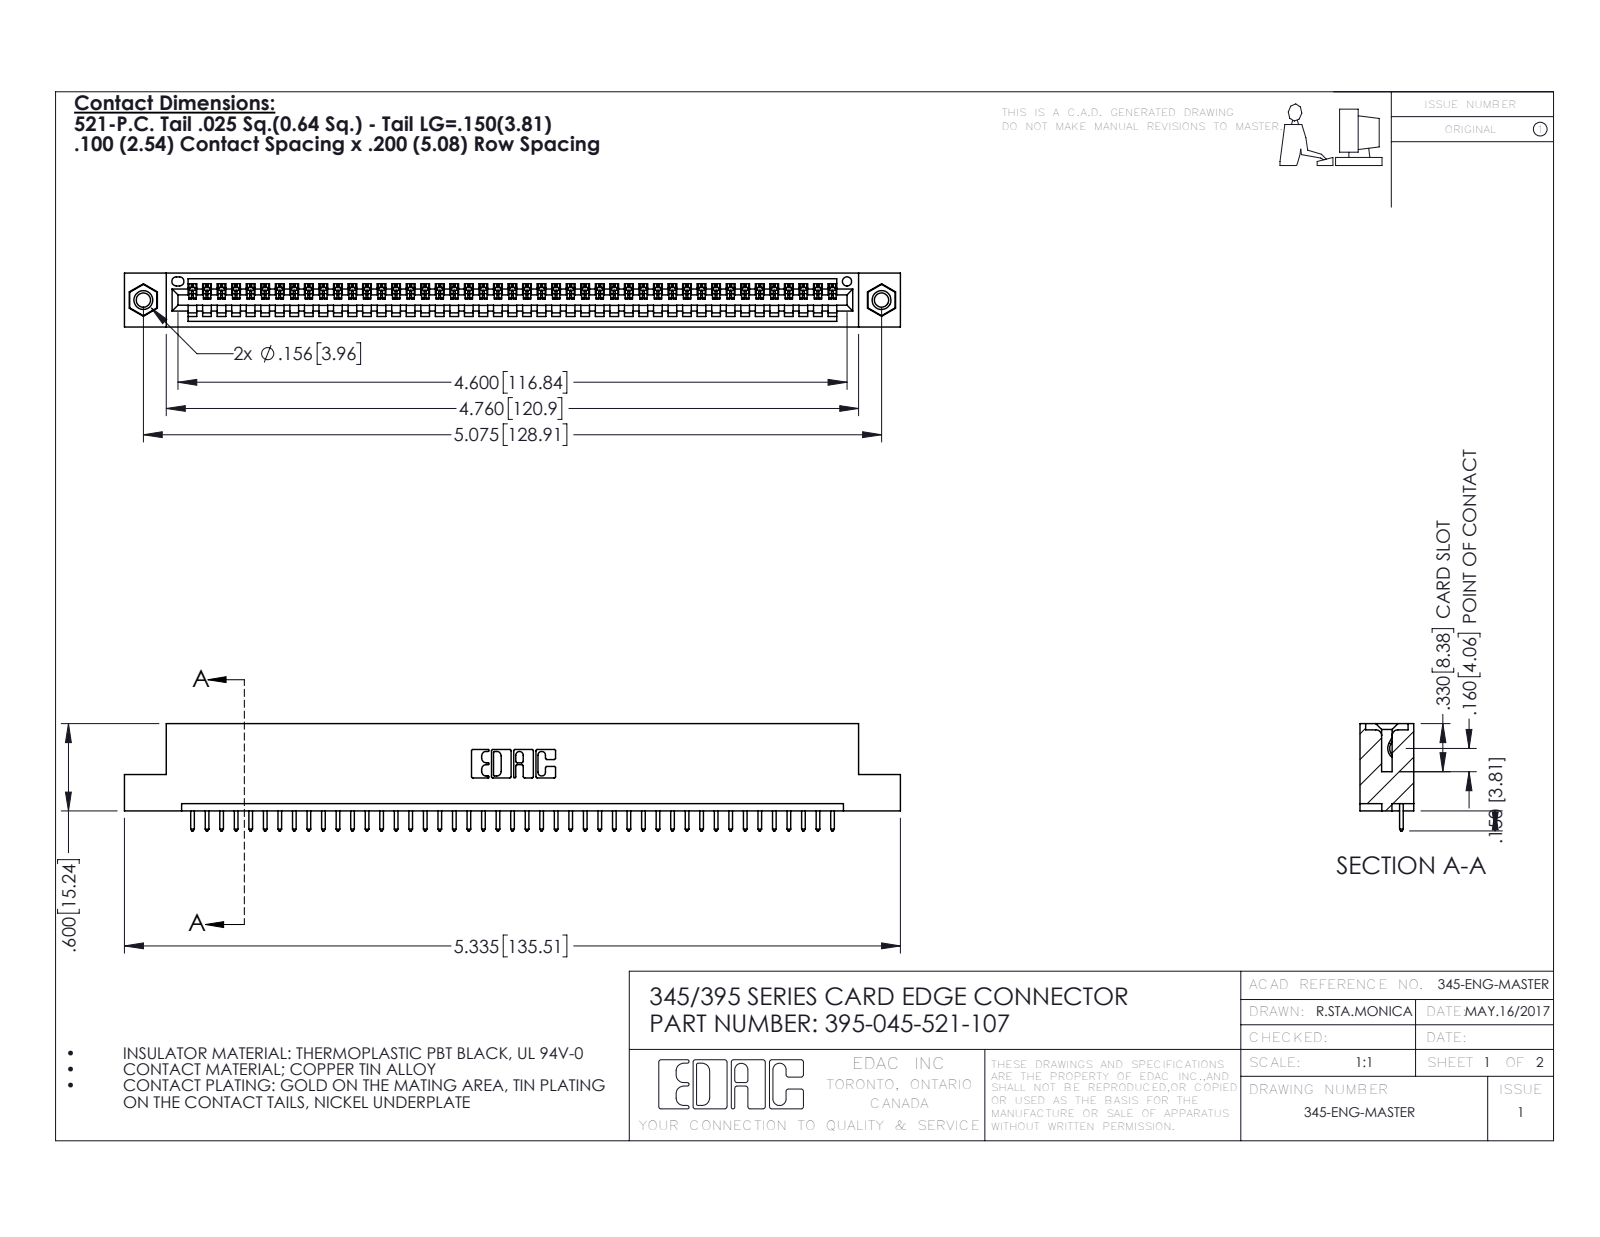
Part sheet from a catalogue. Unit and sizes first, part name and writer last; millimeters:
Units: millimetres
Overall size (bounding box): 135.5 × 18.7 × 9.4
Round holes (diameter × count): ⌀2.5 ×2, ⌀3.2 ×2, ⌀4 ×2, ⌀1.6 ×1
Round bosses / shafts (diameter × count): ⌀3.9 ×2
Partial cylindrical surfaces — rounded edges, fillets, slot ends (radius × count): R0.2 ×90, R0.3 ×90, R0.3 ×22, R0.2 ×6, R0.8 ×6, R0.7 ×3, R0.8 ×2, R1 ×2
Main face-to-face distances: 1.8, 7.6, 9.4, 5.1, 2.5, 6.9, 0.6, 5.7, 3.8, 1.8
Hole centre spacings: 6.9, 122.9, 128.9
Volume: 12 700 mm³ · Surface area: 16 520 mm²
Bodies: 48 solids, 2796 faces (1912 planar, 868 cylindrical, 16 other)
Part name (STEP PRODUCT): 345-250-001_345-250-005-103; 345-292-001_345-293-121; 345 Part_Flush Mounting Lugs - 0.156 Dia-TI; 395-045-521-107
STEP written by: SolidWorks 2016 (CONFIG_CONTROL_DESIGN)
